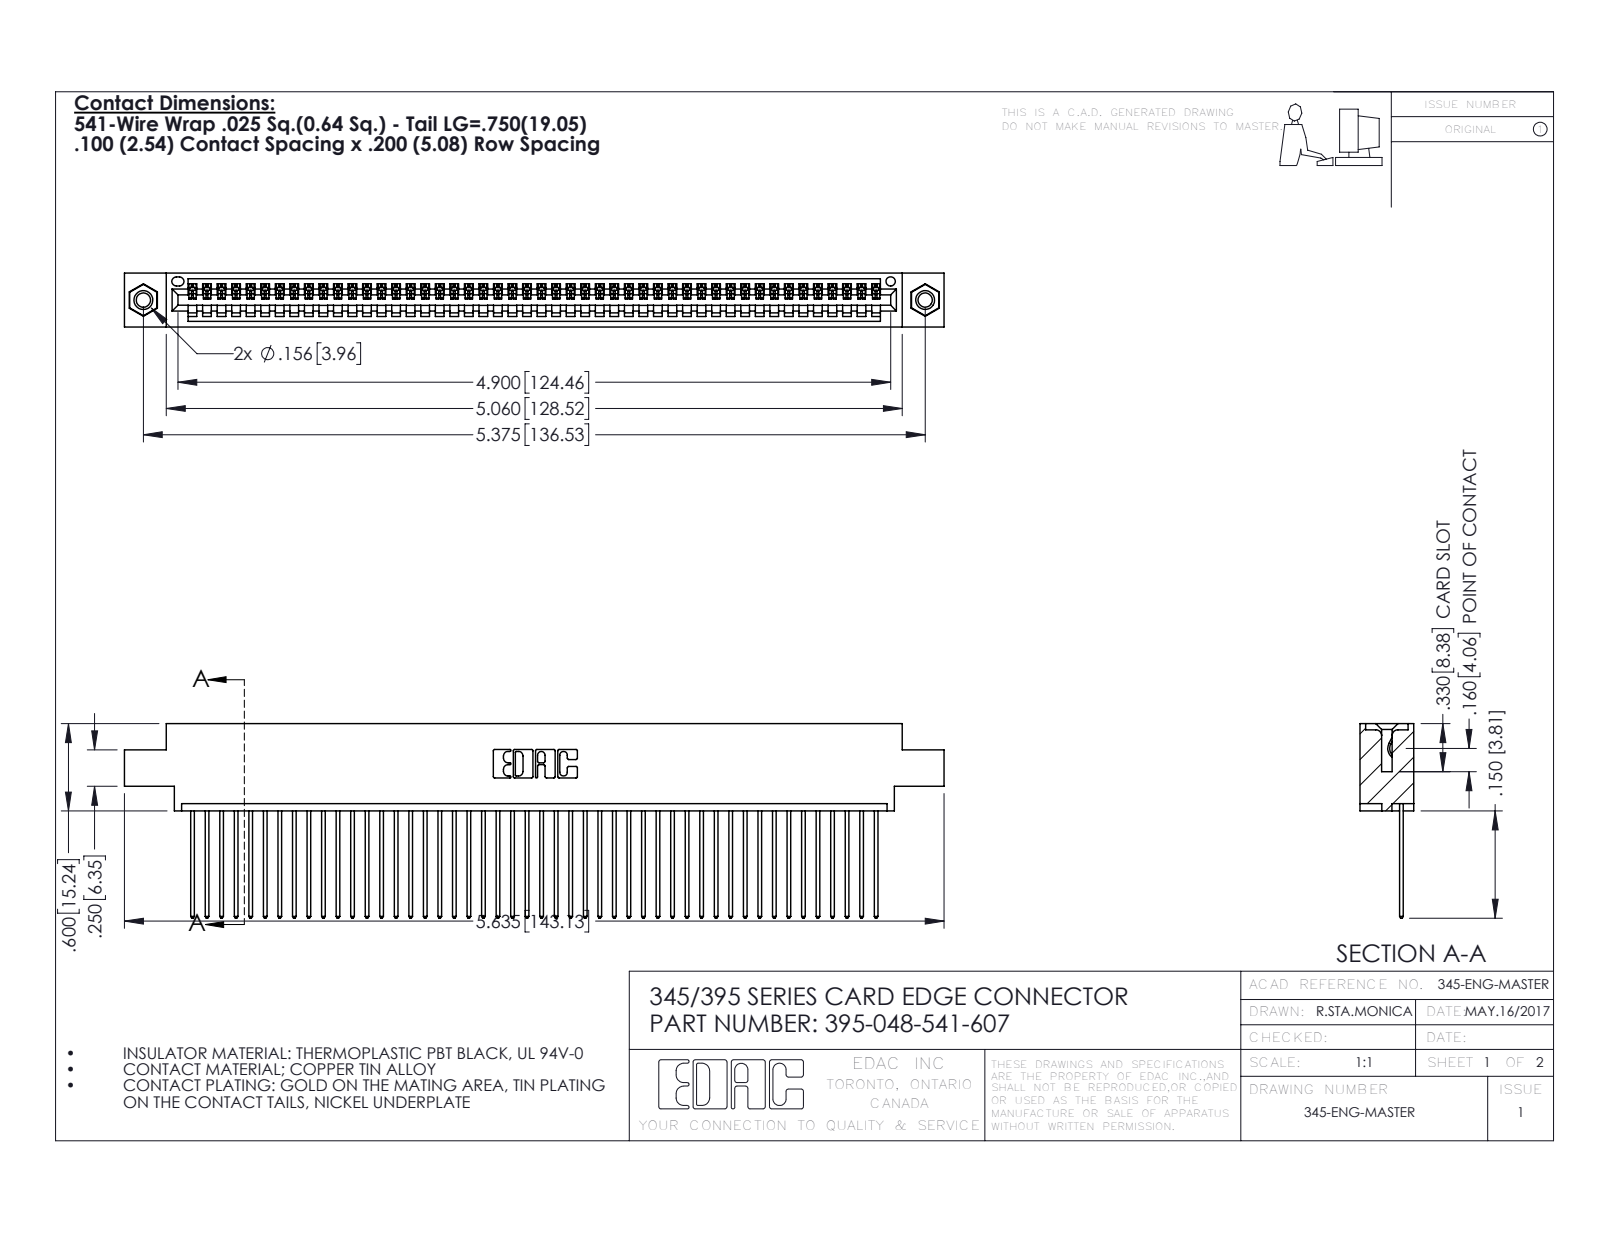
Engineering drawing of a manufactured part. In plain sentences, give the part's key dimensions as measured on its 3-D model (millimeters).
The part is named "395-048-541-607; 345 Part_0.170 Offset - 0.156 Dia-TI; 345-250-001_345-250-005-103; 345-292-001_345-293-141". Its 3-D file was written by "SolidWorks 2016 (CONFIG_CONTROL_DESIGN)". It is 51 solids with 2974 faces: 2036 planar, 922 cylindrical and 16 other. Overall it measures 143.1 by 34 by 9.4 millimeters. Its volume is 13 700 cubic millimeters and its surface area 19 350 square millimeters. Round holes: 2 of diameter 2.5, 2 of diameter 3.2, 2 of diameter 4, 1 of diameter 1.6. Round bosses or shafts: 2 of diameter 3.9. Partial cylindrical surfaces (rounded edges, fillets, slot ends): 96 of radius 0.2, 96 of radius 0.3, 22 of radius 0.3, 6 of radius 0.2, 6 of radius 0.8, 3 of radius 0.7, 2 of radius 0.8, 2 of radius 1. The main face-to-face distances are 1.8, 7.6, 9.4, 2.5, 6.9, 0.6, 5.1, 5.7, 4.4, 3.8. The hole center spacings are 6.9, 130.5, 136.5.
